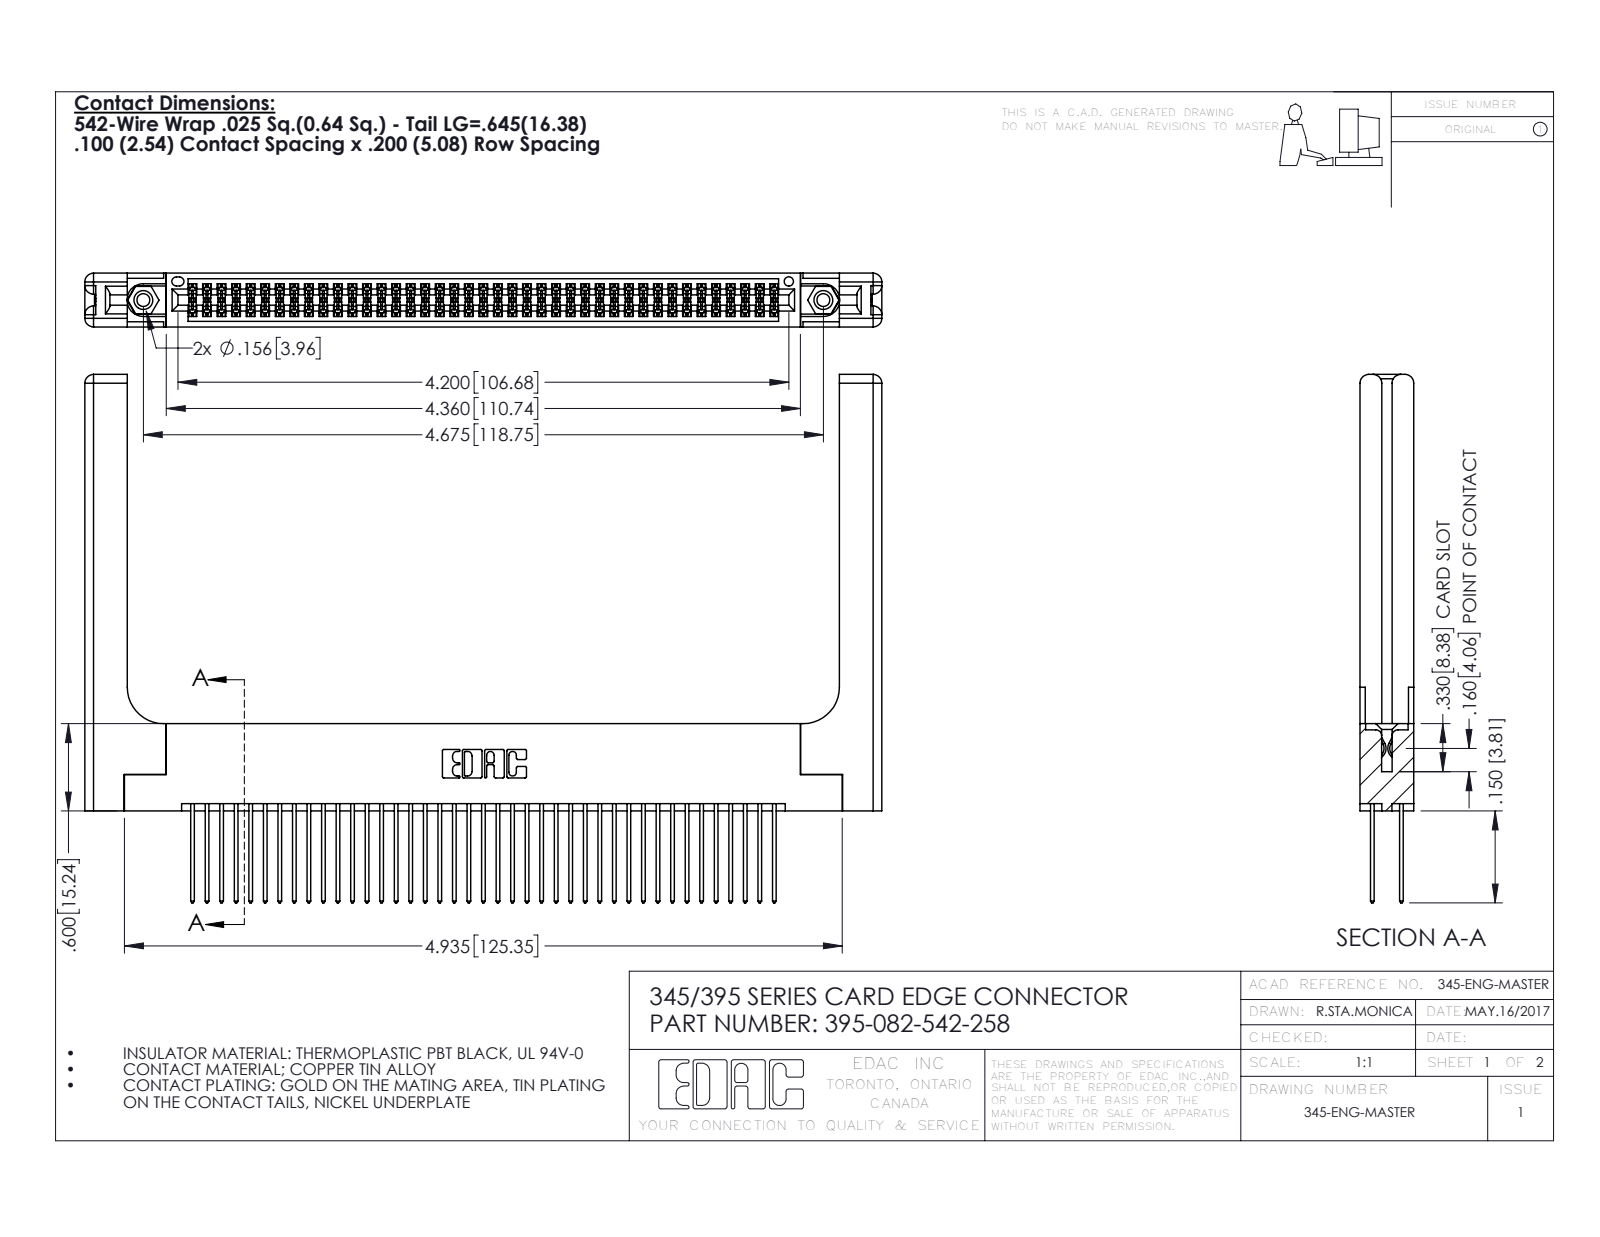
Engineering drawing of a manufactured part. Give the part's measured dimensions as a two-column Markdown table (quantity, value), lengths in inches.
| quantity | value |
| --- | --- |
| part name | 345 Part_Flush Mounting Lugs - 0.156 Dia-TH; 395-082-542-258; 345-250-001_345-250-001-102; 345-220-058_345-220-058 (+1 more) |
| STEP written by | SolidWorks 2016 (CONFIG_CONTROL_DESIGN) |
| units | inches |
| bodies | 87 solids, 4482 faces (2934 planar, 1488 cylindrical, 60 other) |
| overall size | 5.479 × 3.632 × 0.37 |
| volume | 1.365 in³ |
| surface area | 42.41 in² |
| round holes (diameter × count) | 0.089 × 2, 0.125 × 2, 0.156 × 2, 0.064 × 1 |
| round bosses / shafts (diameter × count) | 0.155 × 2 |
| partial cylindrical surfaces (radius × count) | 0.006 × 123, 0.01 × 82, 0.01 × 22, 0.06 × 16, 0.007 × 6, 0.031 × 6, 0.026 × 3, 0.014 × 2 |
| main face-to-face distances | 0.072, 0.298, 0.37, 0.2, 0.098, 0.272, 0.025, 0.225, 0.175, 0.148 |
| hole center spacings | 0.27, 4.439, 4.675 |
